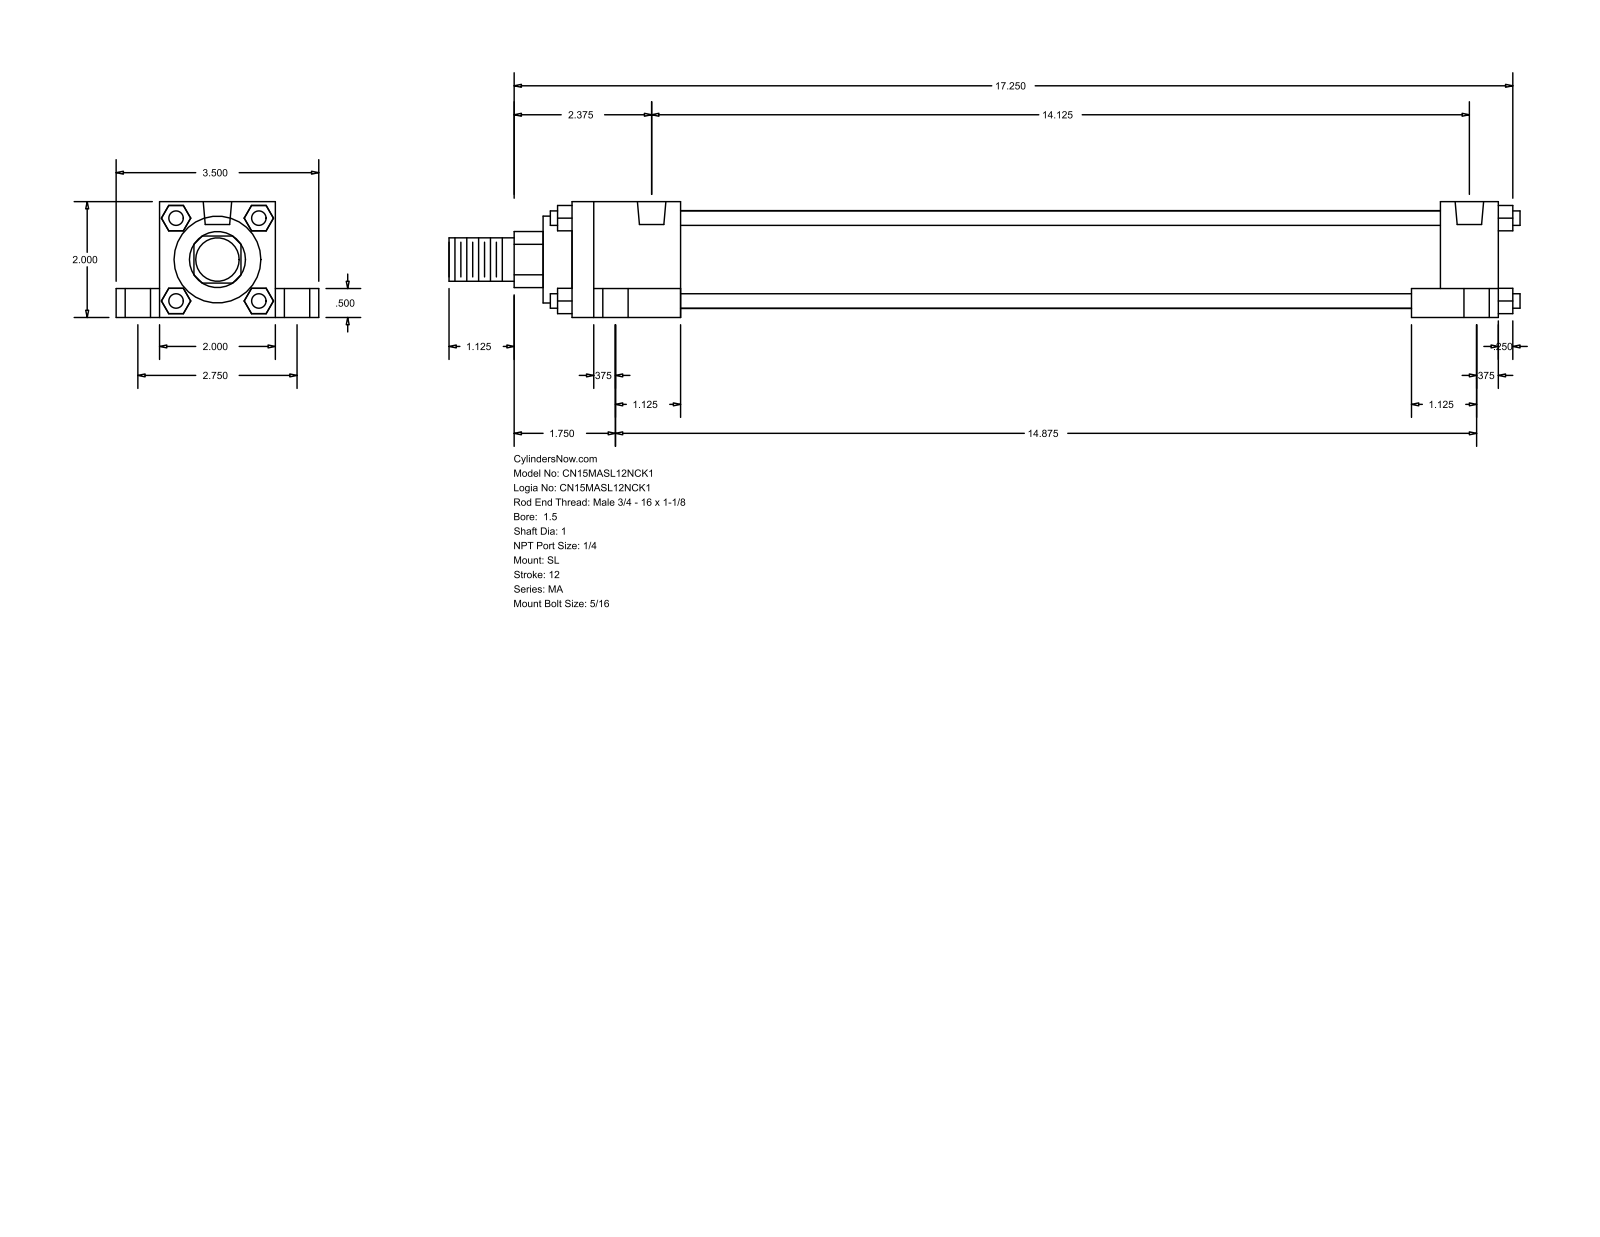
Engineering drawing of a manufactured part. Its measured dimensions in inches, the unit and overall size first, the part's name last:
Units: inches
Overall size (bounding box): 18.5 × 3.5 × 2
Round holes (diameter × count): ⌀0.313 ×4, ⌀0.437 ×4, ⌀0.687 ×4, ⌀0.492 ×2
Round bosses / shafts (diameter × count): ⌀0.25 ×4, ⌀1.69 ×1, ⌀1.5 ×1, ⌀1 ×1, ⌀0.75 ×1
Partial cylindrical surfaces — rounded edges, fillets, slot ends (radius × count): R0.484 ×1
Main face-to-face distances: 2, 0.5, 0.75, 2.75, 1.5, 0.375, 16, 1, 0.25, 15
Hole centre spacings: 1.38, 1.51, 2.75, 14.125, 14.316, 14.814, 14.875, 15.127
Bodies: 0 solids, 148 faces (112 planar, 36 cylindrical, 0 other)
Part name (STEP PRODUCT): MA_SL__0150_1
STEP written by: GSSL Pune (CONFIG_CONTROL_DESIGN)
